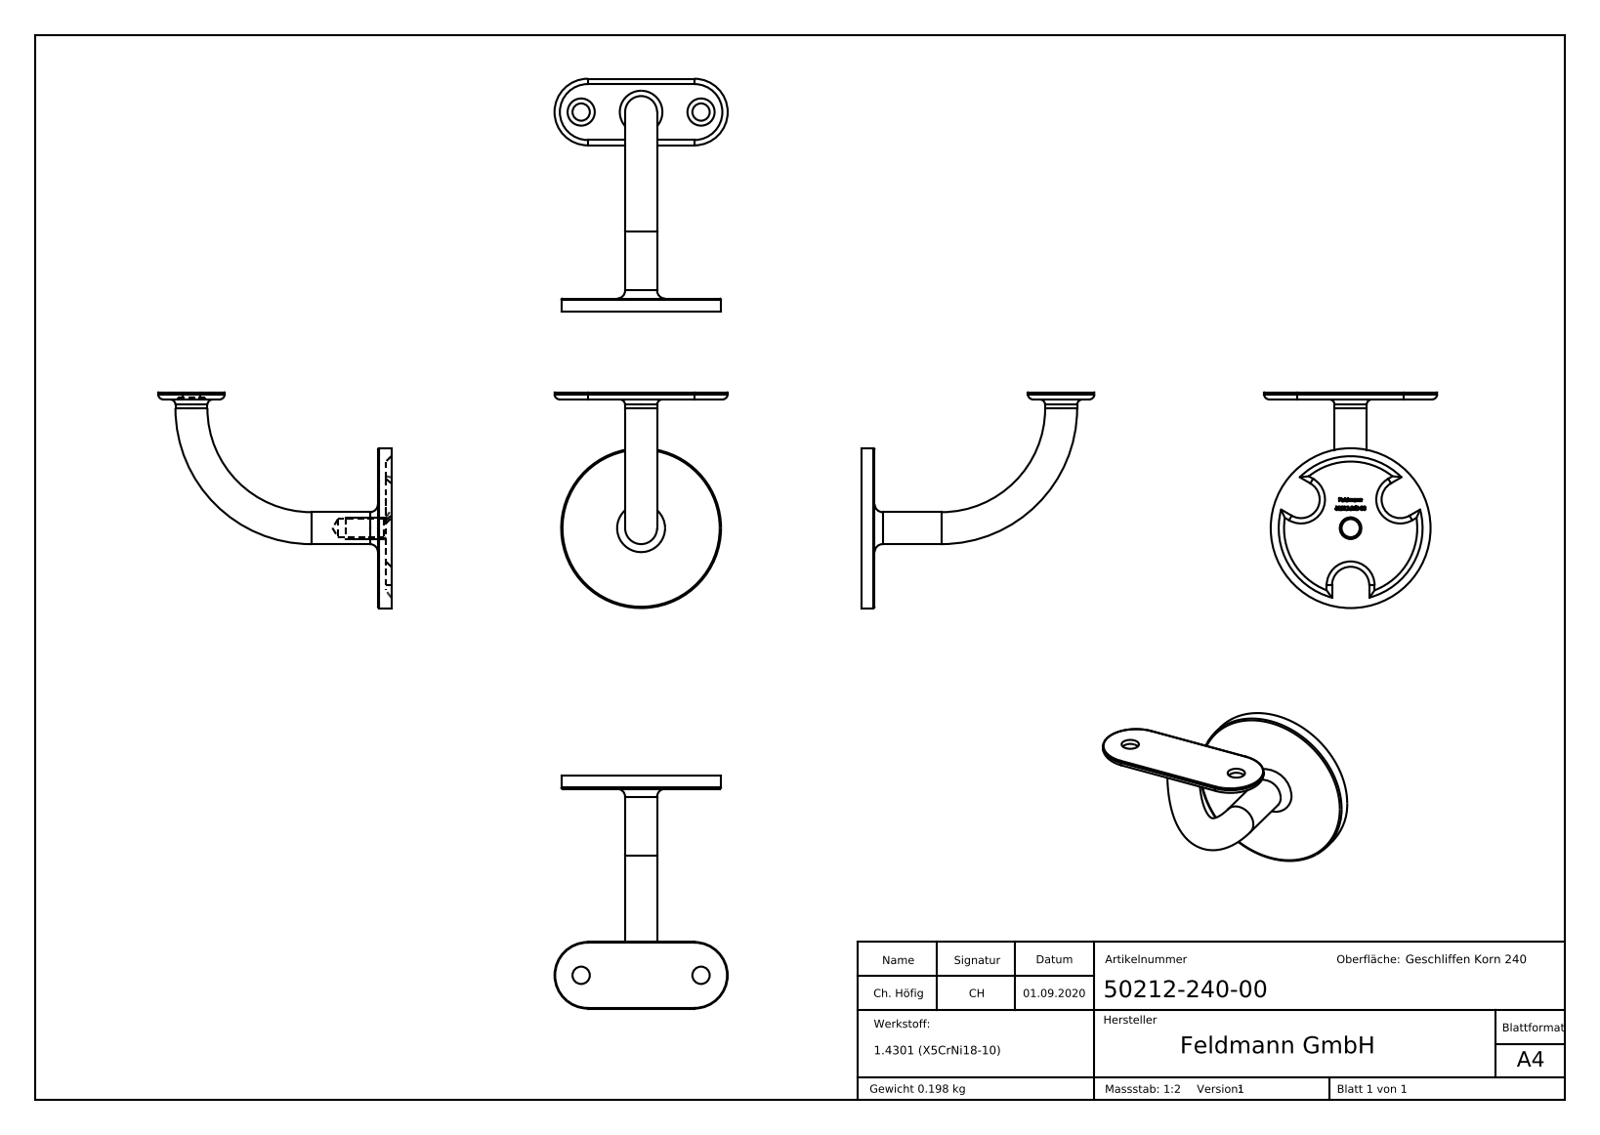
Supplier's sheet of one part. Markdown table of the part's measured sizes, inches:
| quantity | value |
| --- | --- |
| part name | 50212-240-00 |
| STEP written by | SolidWorks 2018 (CONFIG_CONTROL_DESIGN) |
| units | inches |
| bodies | 1 solid, 304 faces (148 planar, 22 cylindrical, 134 other) |
| overall size | 3.445 × 3.189 × 2.559 |
| volume | 1.533 in³ |
| surface area | 21.4 in² |
| round holes (diameter × count) | 0.256 × 2, 0.402 × 2, 0.268 × 1 |
| round bosses / shafts (diameter × count) | 0.472 × 2, 2.362 × 1 |
| partial cylindrical surfaces (radius × count) | 0.01 × 2, 0.079 × 2, 0.492 × 2 |
| main face-to-face distances | 0.118, 0.079, 0.197, 0.106, 0.035, 0.071, 3.445, 3.366, 3.248, 2.461 |
| hole center spacings | 1.772 |
